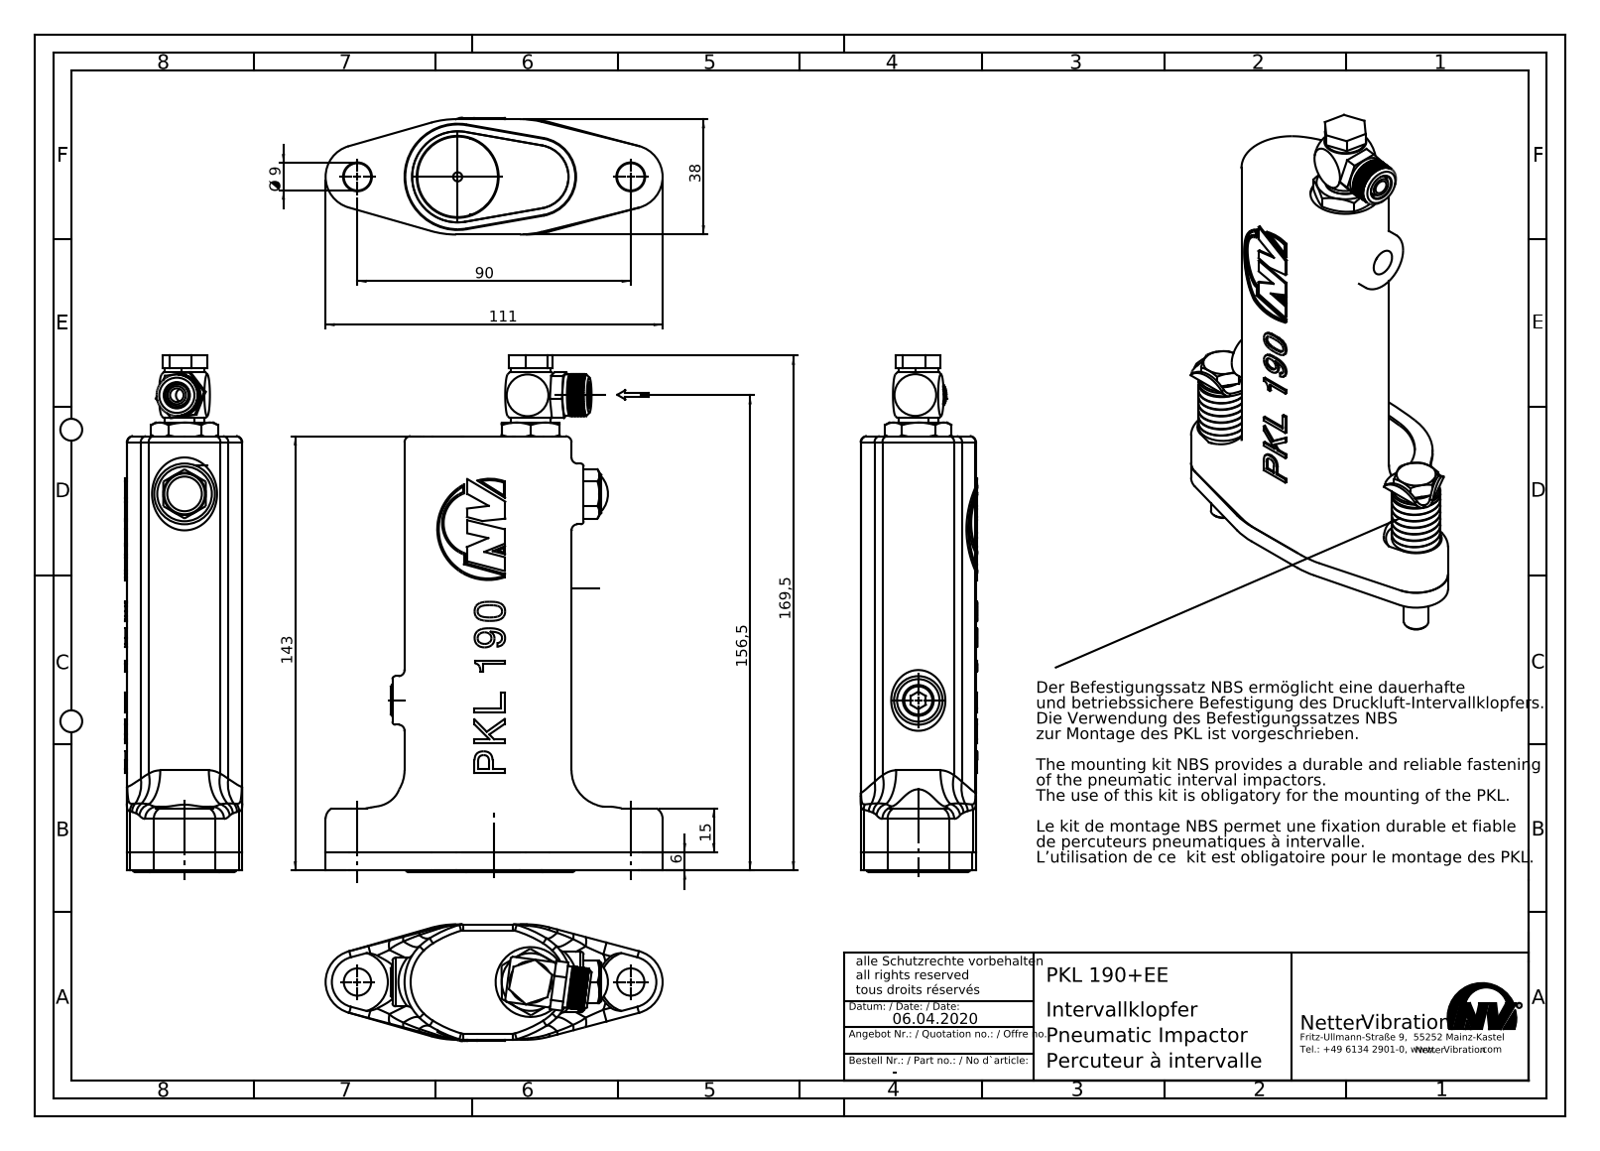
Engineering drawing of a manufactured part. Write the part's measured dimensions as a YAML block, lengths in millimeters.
part_name: "PKL 190 EE"
step_written_by: "SolidWorks 2015 (AUTOMOTIVE_DESIGN)"
units: millimeters
bodies: {solids: 13, faces: 1992, planar: 475, cylindrical: 514, other: 1003}
overall_size: [183.4, 111, 47.5]
volume: 296929
surface_area: 63221
round_holes:
  - {diameter: 3.5, count: 2}
  - {diameter: 4.5, count: 2}
  - {diameter: 8.4, count: 2}
  - {diameter: 8.5, count: 2}
  - {diameter: 8.57, count: 2}
  - {diameter: 9, count: 2}
  - {diameter: 9.5, count: 2}
  - {diameter: 11.45, count: 2}
  - {diameter: 3, count: 1}
  - {diameter: 8.3, count: 1}
  - {diameter: 10, count: 1}
  - {diameter: 10.1, count: 1}
round_bosses_or_shafts:
  - {diameter: 16, count: 3}
  - {diameter: 13, count: 3}
  - {diameter: 9.73, count: 2}
  - {diameter: 8, count: 2}
  - {diameter: 26.5, count: 1}
  - {diameter: 20, count: 1}
  - {diameter: 16.66, count: 1}
  - {diameter: 13.65, count: 1}
partial_cylinders:
  - {radius: 4, count: 8}
  - {radius: 30, count: 8}
  - {radius: 10.5, count: 7}
  - {radius: 1, count: 5}
  - {radius: 19.65, count: 4}
  - {radius: 40, count: 4}
  - {radius: 2, count: 3}
  - {radius: 9, count: 2}
face_to_face_distances: [6, 38, 143, 137, 1, 0.5, 101.9, 44.12, 1.7, 40.1]
hole_center_spacings: [33, 57, 24, 37, 90]
